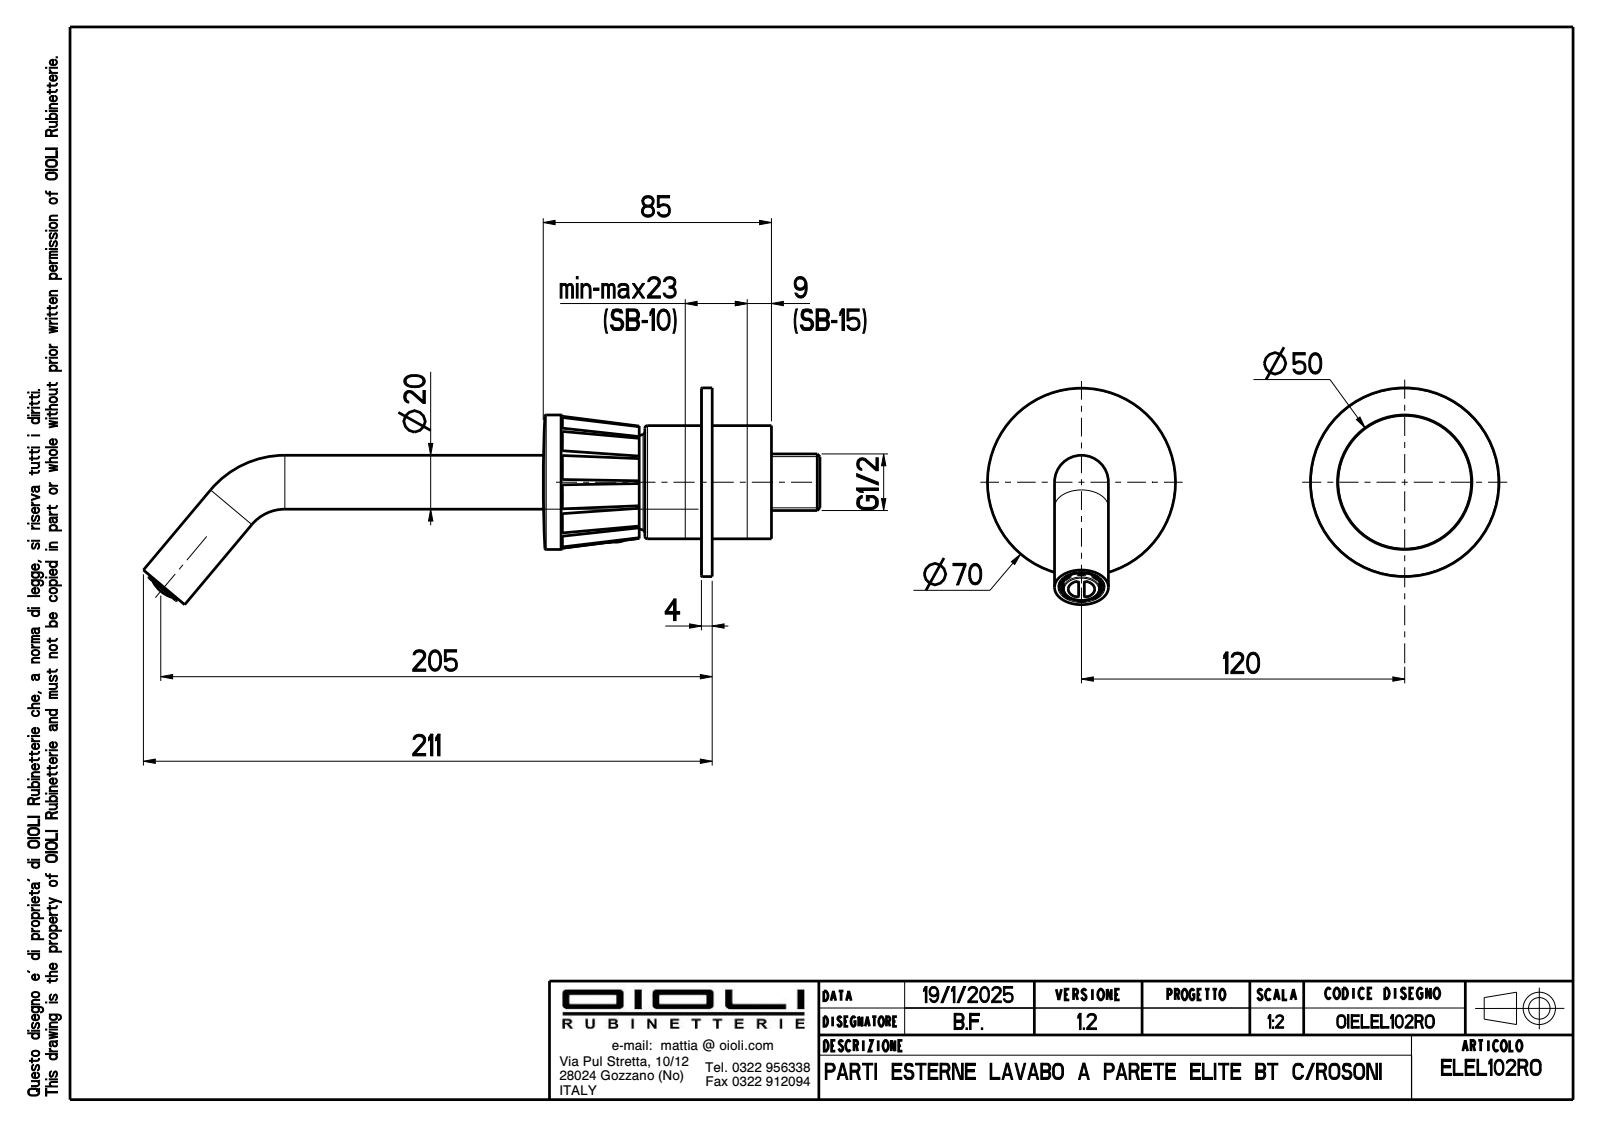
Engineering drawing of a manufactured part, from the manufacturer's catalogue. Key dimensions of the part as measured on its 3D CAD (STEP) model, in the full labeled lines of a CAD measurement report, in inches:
Part name (STEP PRODUCT): OIBR00949; OIBR00242; OIBR00144; OICT00088 (+5 more)
STEP written by: CREO PARAMETRIC BY PTC INC, 2024493 (CONFIG_CONTROL_DESIGN)
Units: inches
Bodies: 9 solids, 907 faces (557 planar, 147 cylindrical, 203 other)
Overall size (bounding box): 10.894 × 7.476 × 4.701
Volume: 5.61 in³ · Surface area: 109.4 in²
Round holes (diameter × count): ⌀0.165 ×2, ⌀0.551 ×2, ⌀0.61 ×2, ⌀0.157 ×1, ⌀0.209 ×1, ⌀0.256 ×1, ⌀0.374 ×1, ⌀0.571 ×1, ⌀0.573 ×1, ⌀0.659 ×1, ⌀0.669 ×1, ⌀1.181 ×1
Round bosses / shafts (diameter × count): ⌀0.65 ×3, ⌀0.787 ×2, ⌀0.197 ×2, ⌀2.756 ×1, ⌀2.748 ×1, ⌀1.965 ×1, ⌀1.654 ×1, ⌀1.24 ×1
Partial cylindrical surfaces — rounded edges, fillets, slot ends (radius × count): R0.004 ×14, R0.035 ×8, R0.024 ×4, R0.018 ×3, R0.268 ×2, R0.098 ×1, R0.265 ×1, R0.294 ×1
Main face-to-face distances: 0.138, 0.413, 0.275, 0.57, 0.433, 0.157, 9.142, 9.004, 8.729, 8.571
Hole centre spacings: 4.724, 7.467, 7.476
